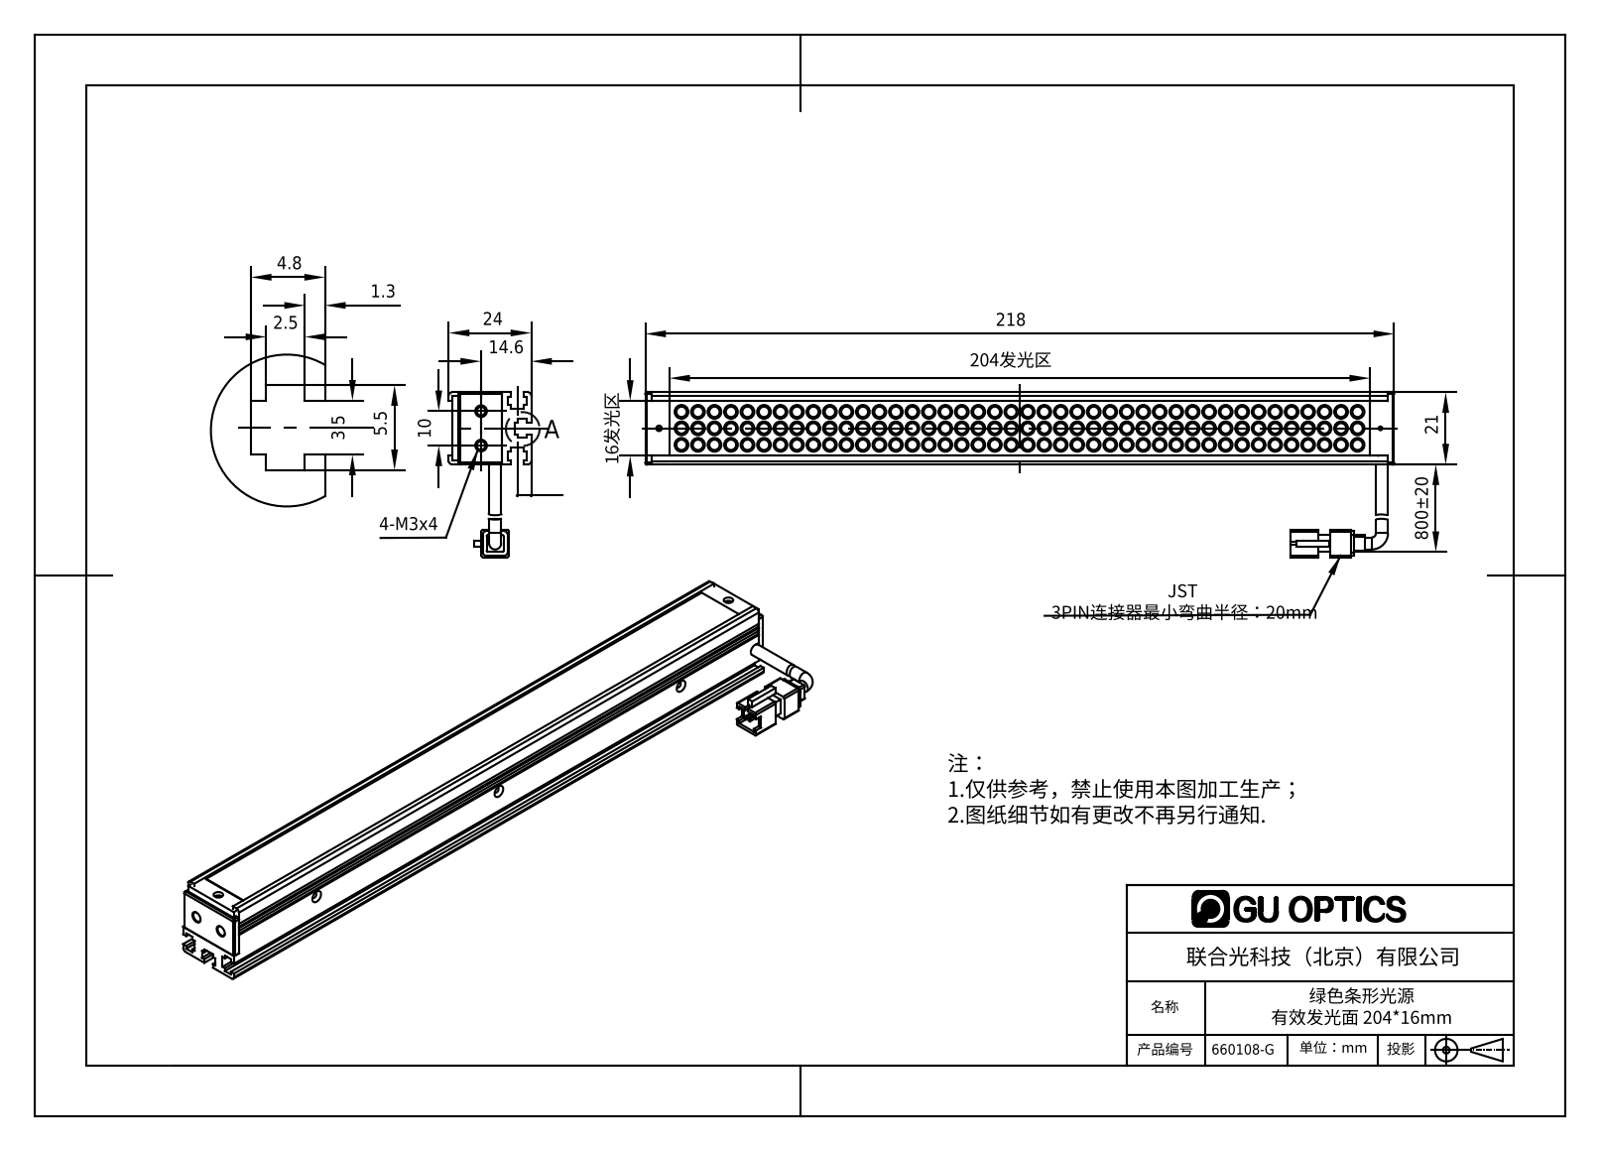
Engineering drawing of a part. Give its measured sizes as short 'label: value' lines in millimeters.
name: 660108-G
written by: SolidWorks 2016 (AUTOMOTIVE_DESIGN)
unit: mm
bodies: 8 solids, 1201 faces (377 planar, 591 cylindrical, 233 other)
size: 218 × 48 × 24
volume: 62 599 mm³; area: 69 705 mm²
holes: 5× ⌀1.6, 3× ⌀1.7, 2× ⌀1.5, 2× ⌀2.5, 2× ⌀2.8, 2× ⌀3, 1× ⌀1.1, 1× ⌀1.25, 1× ⌀2
bosses: 126× ⌀4, 126× ⌀3, 2× ⌀3.5
rounds: 12× R1, 8× R0.5, 1× R1.65
face distances: 1, 2.5, 2, 18.5, 21, 4, 3.5, 2.3, 21.1, 23.1
hole spacings: 210, 7, 30.04, 30.48, 75, 105.01, 105.14, 180.01
